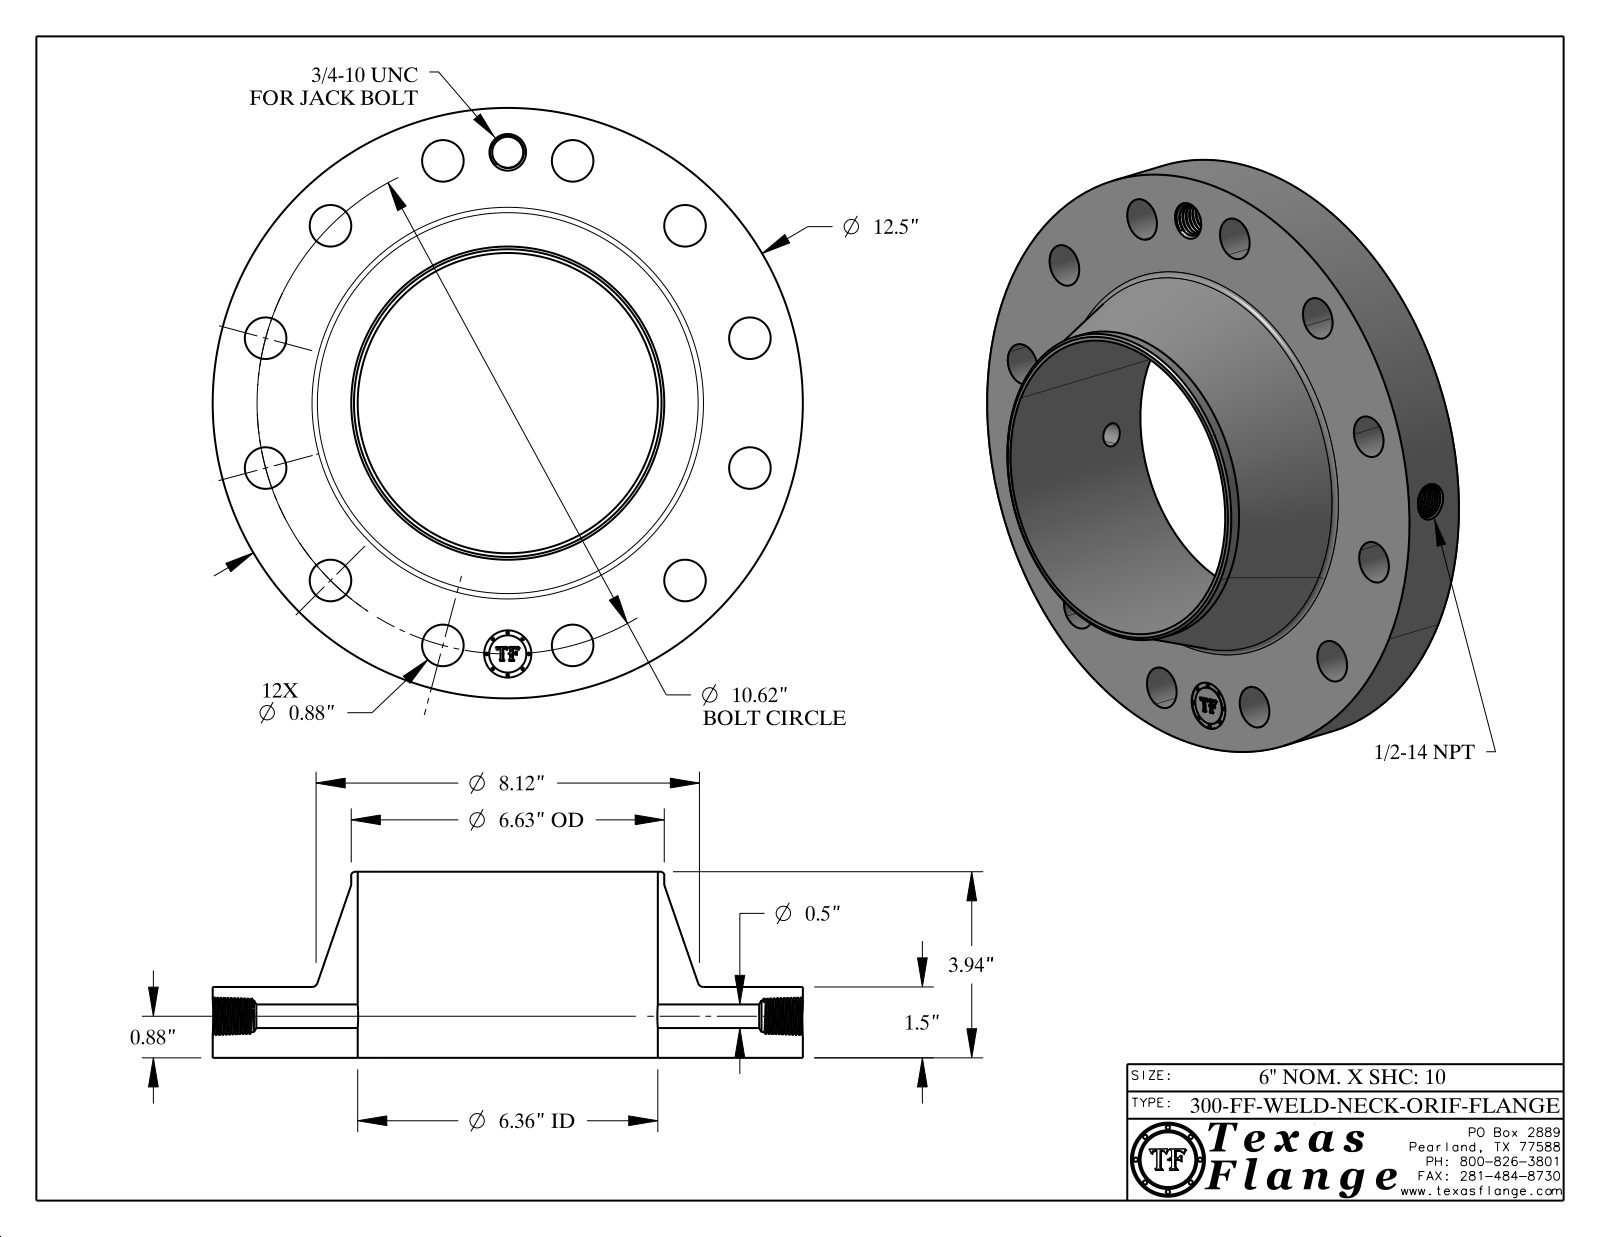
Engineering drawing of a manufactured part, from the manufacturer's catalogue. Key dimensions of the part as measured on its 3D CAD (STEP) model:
Part name (STEP PRODUCT): 300-FF-WELD-NECK
STEP written by: CATIA V5 STEP AP214 (AUTOMOTIVE_DESIGN)
Units: inches
Bodies: 1 solid, 770 faces (368 planar, 98 cylindrical, 304 other)
Overall size (bounding box): 12.5 × 12.5 × 3.94
Volume: 148.1 in³ · Surface area: 411.9 in²
Round holes (diameter × count): ⌀0.88 ×12, ⌀0.5 ×1, ⌀0.656 ×1, ⌀0.672 ×1, ⌀1 ×1, ⌀6.357 ×1
Round bosses / shafts (diameter × count): ⌀0.061 ×8, ⌀12.5 ×1, ⌀6.63 ×1, ⌀0.788 ×1
Main face-to-face distances: 1.5, 3.94, 2.44, 0.015, 1.485, 2.455, 0.298, 0.293, 0.054, 0.248
Hole centre spacings: 5.31, 7.509, 9.197, 10.258, 5.31, 2.748, 10.62, 1.386
